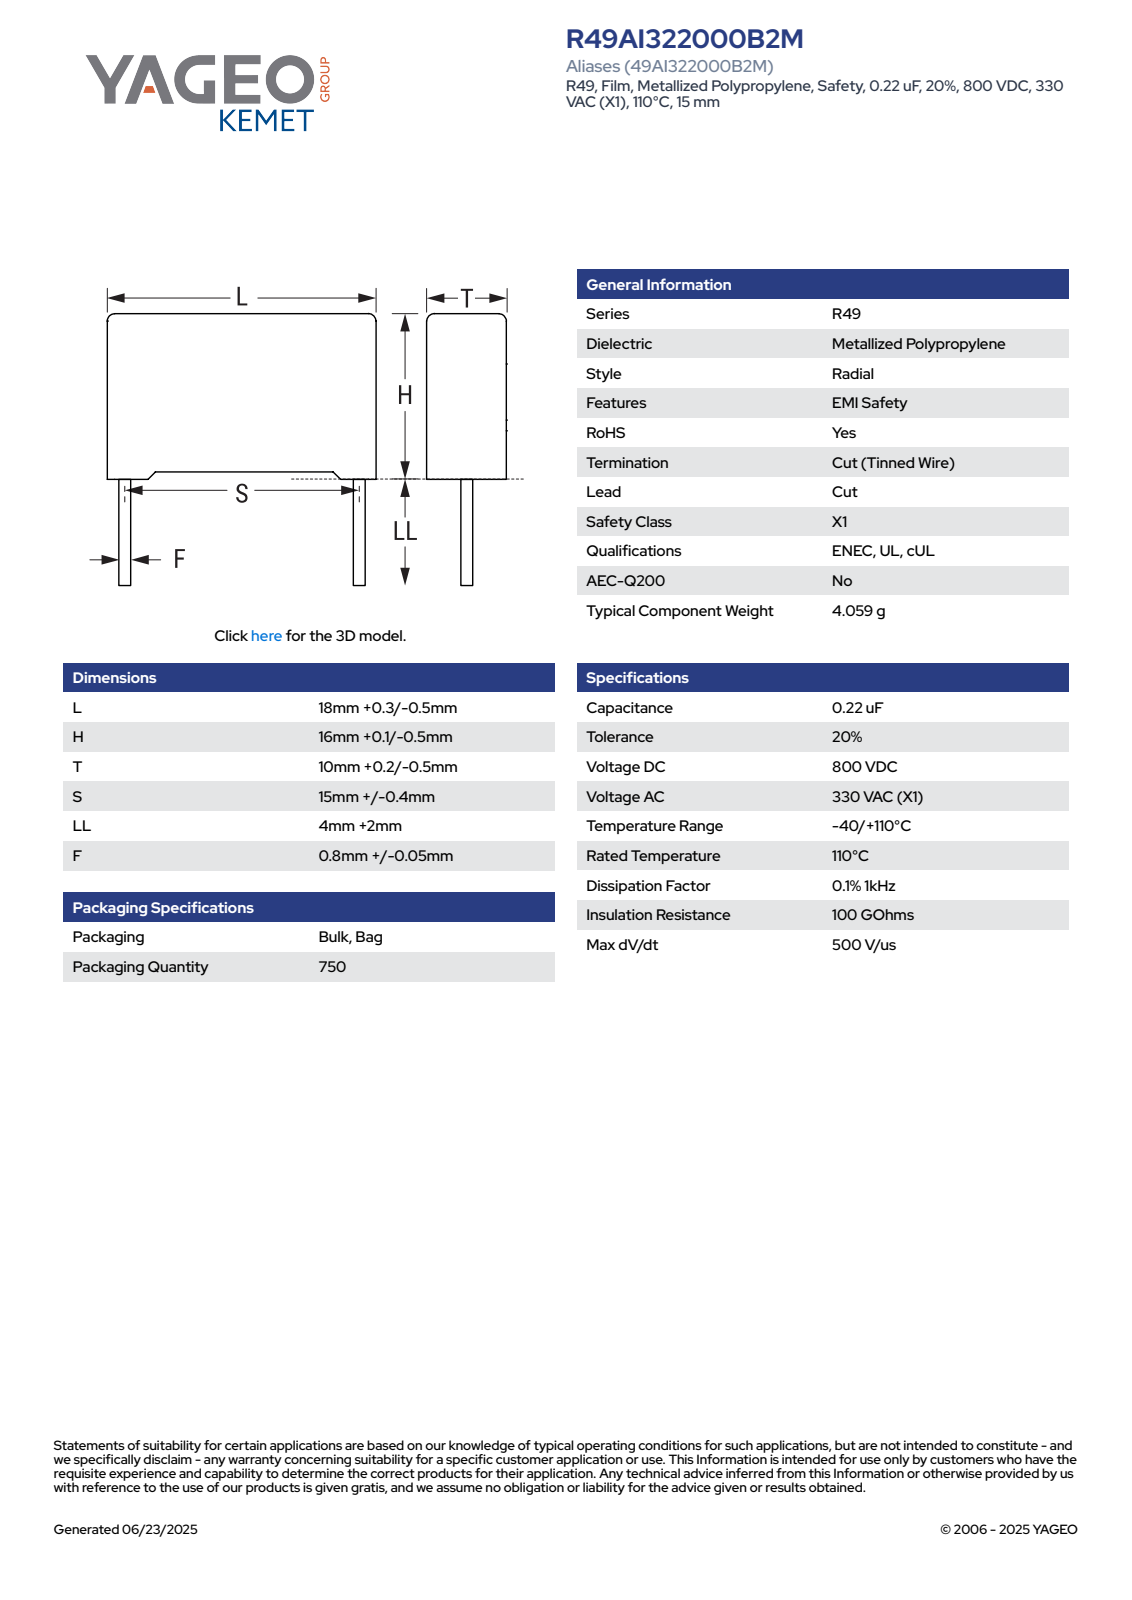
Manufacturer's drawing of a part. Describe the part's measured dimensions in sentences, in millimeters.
The part is named "CFR_RB2_18X16X10_L18.3H16.1T10.2S15LL6F0.85". Its 3-D file was written by "SolidWorks 2021 (AUTOMOTIVE_DESIGN)". It is 4 solids with 85 faces: 77 planar, 8 cylindrical and 0 other. Overall it measures 22.1 by 18.3 by 10.21 millimeters. Its volume is 2 887 cubic millimeters and its surface area 1 354 square millimeters. Round bosses or shafts: 2 of diameter 0.85. Partial cylindrical surfaces (rounded edges, fillets, slot ends): 4 of radius 0.5. The main face-to-face distances are 10.2, 18.3, 15.35, 0.61, 0.75, 16.1, 17.69, 0.56, 15.54, 9.59.
